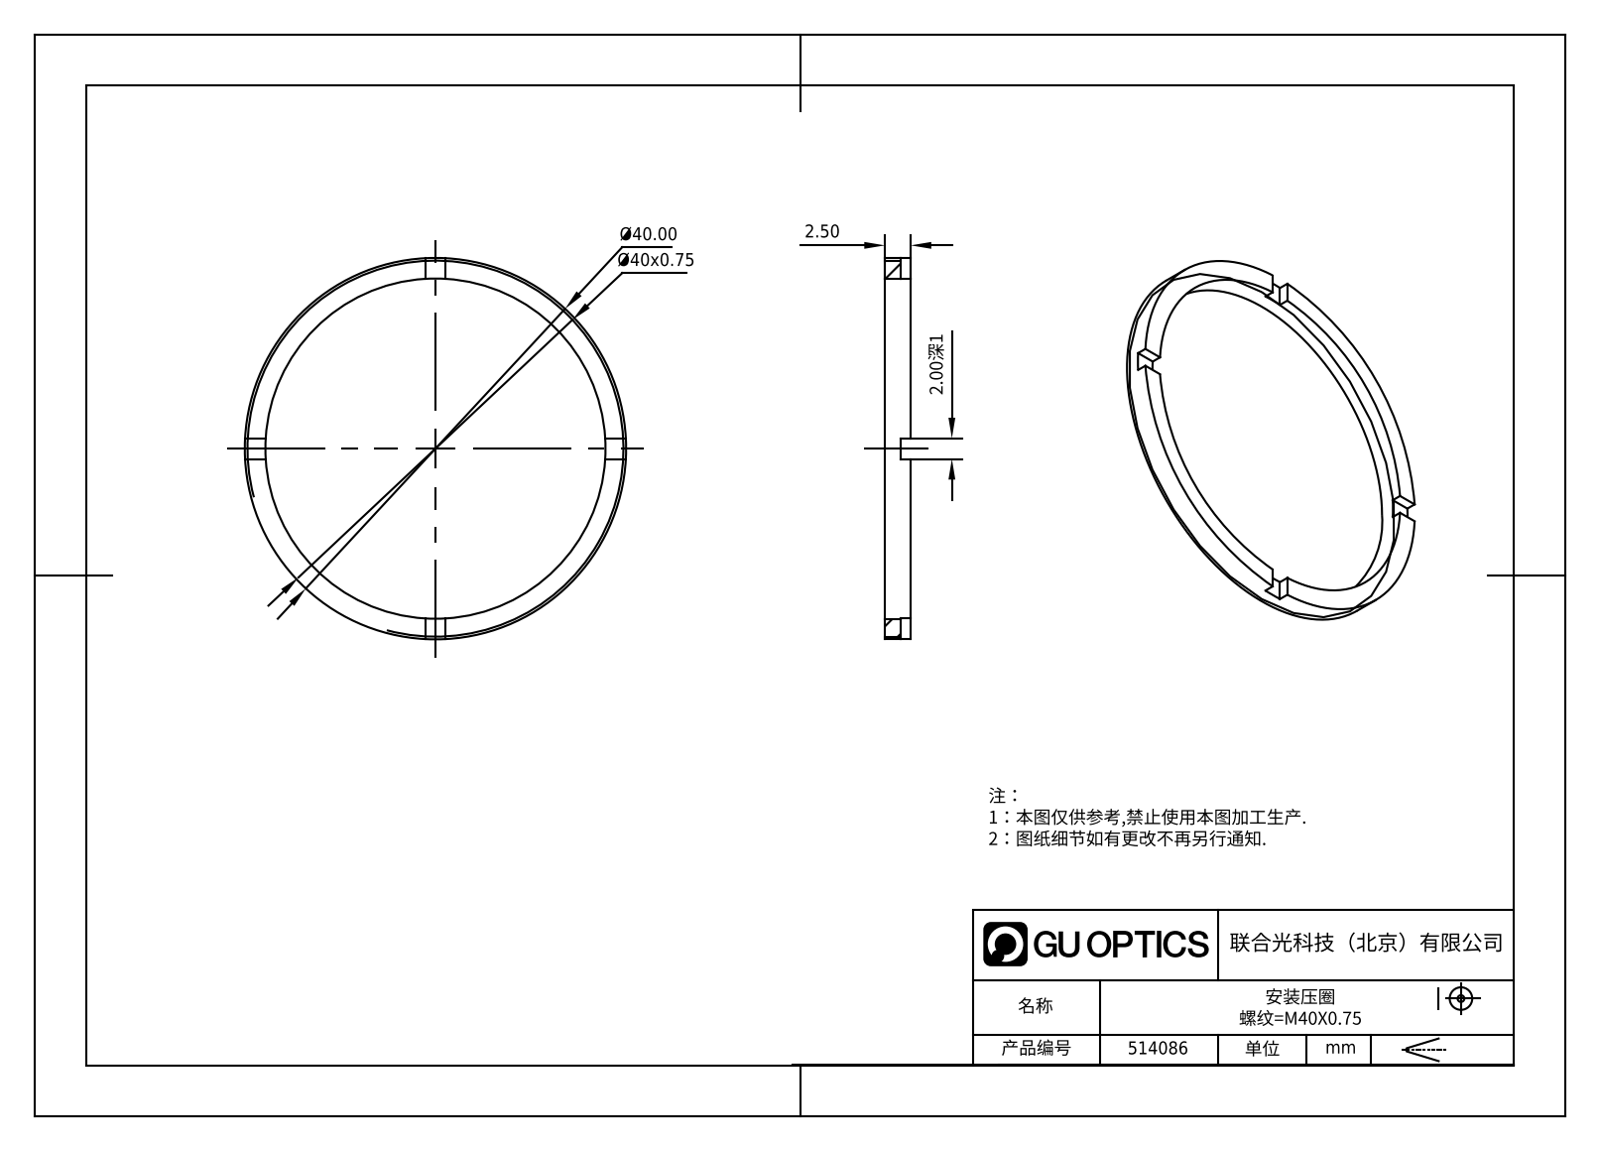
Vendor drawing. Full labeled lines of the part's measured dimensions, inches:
Part name (STEP PRODUCT): 514086
STEP written by: SolidWorks 2020 (CONFIG_CONTROL_DESIGN)
Units: inches
Bodies: 1 solid, 21 faces (17 planar, 4 cylindrical, 0 other)
Overall size (bounding box): 1.575 × 1.575 × 0.098
Volume: 0.035 in³ · Surface area: 1.665 in²
Round holes (diameter × count): ⌀1.417 ×1
Round bosses / shafts (diameter × count): ⌀1.575 ×1
Main face-to-face distances: 0.098, 0.059, 0.039, 0.079
